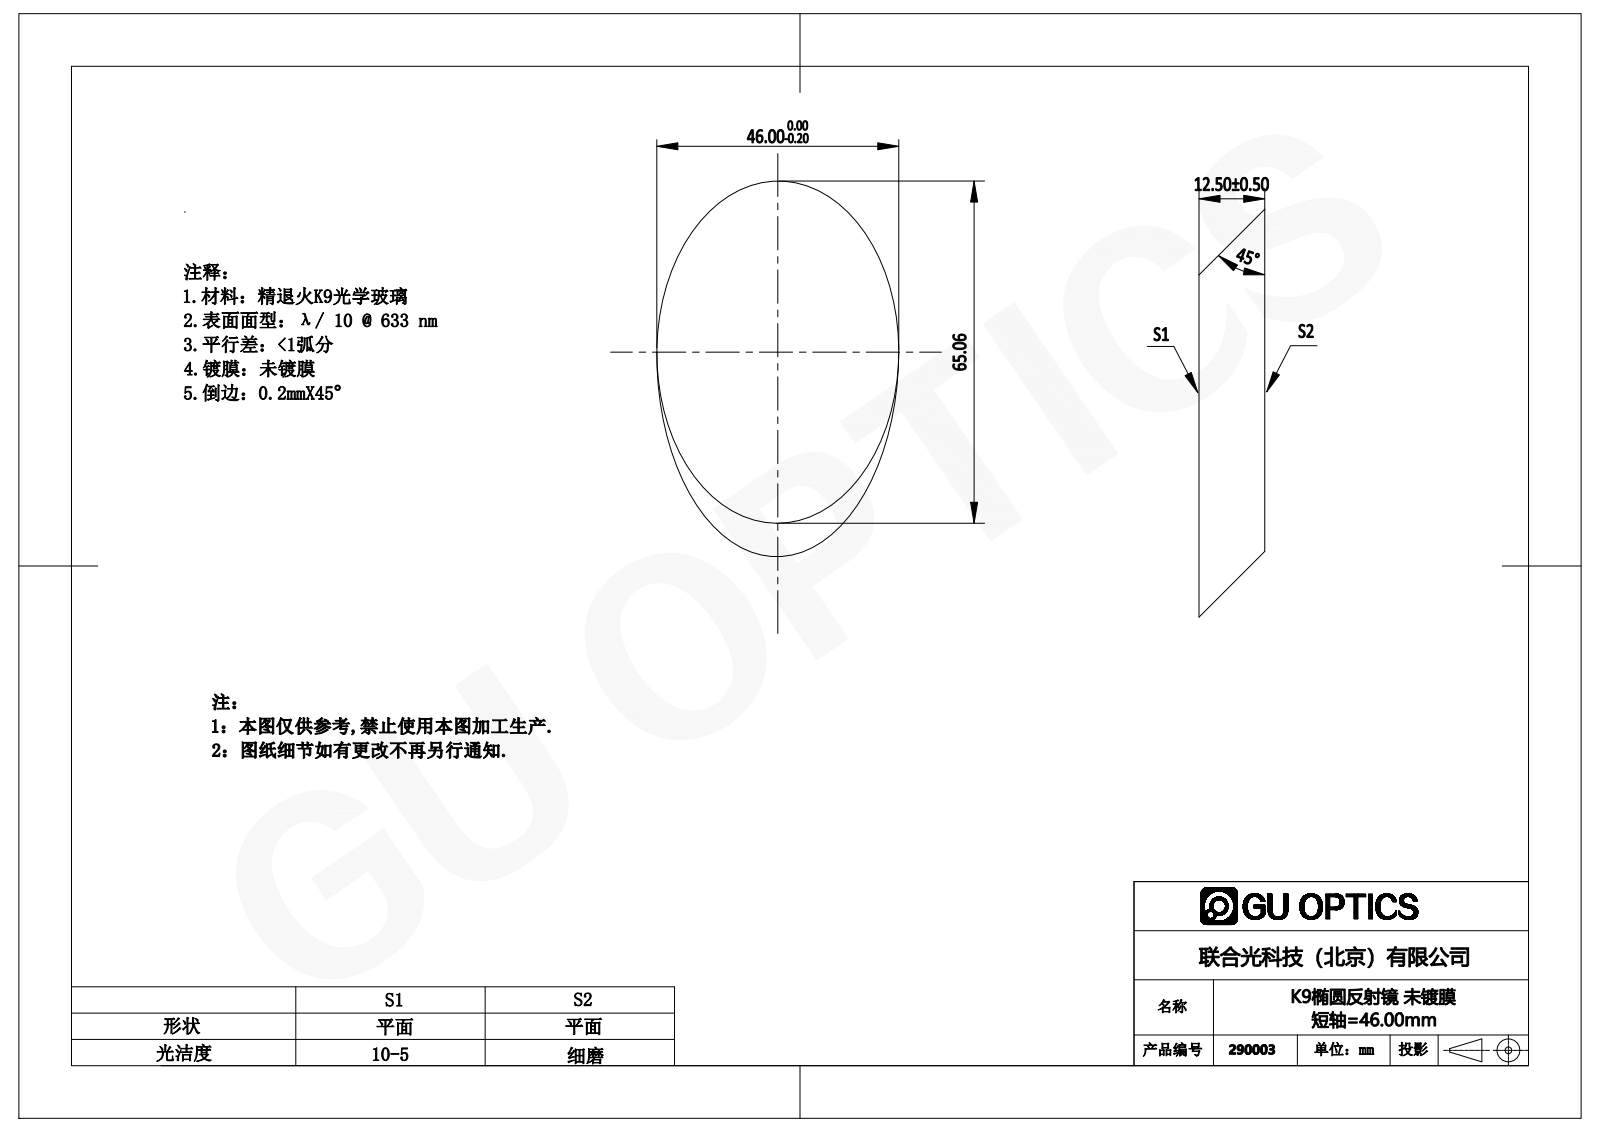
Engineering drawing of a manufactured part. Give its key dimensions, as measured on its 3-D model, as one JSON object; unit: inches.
{"part_name": "290003", "step_written_by": "SolidWorks 2016 (AUTOMOTIVE_DESIGN)", "units": "inches", "bodies": {"solids": 1, "faces": 4, "planar": 2, "cylindrical": 0, "other": 2}, "overall_size": [3.054, 1.811, 0.492], "volume_in3": 1.793, "surface_area_in2": 11.25, "face_to_face_distances": [0.492]}
